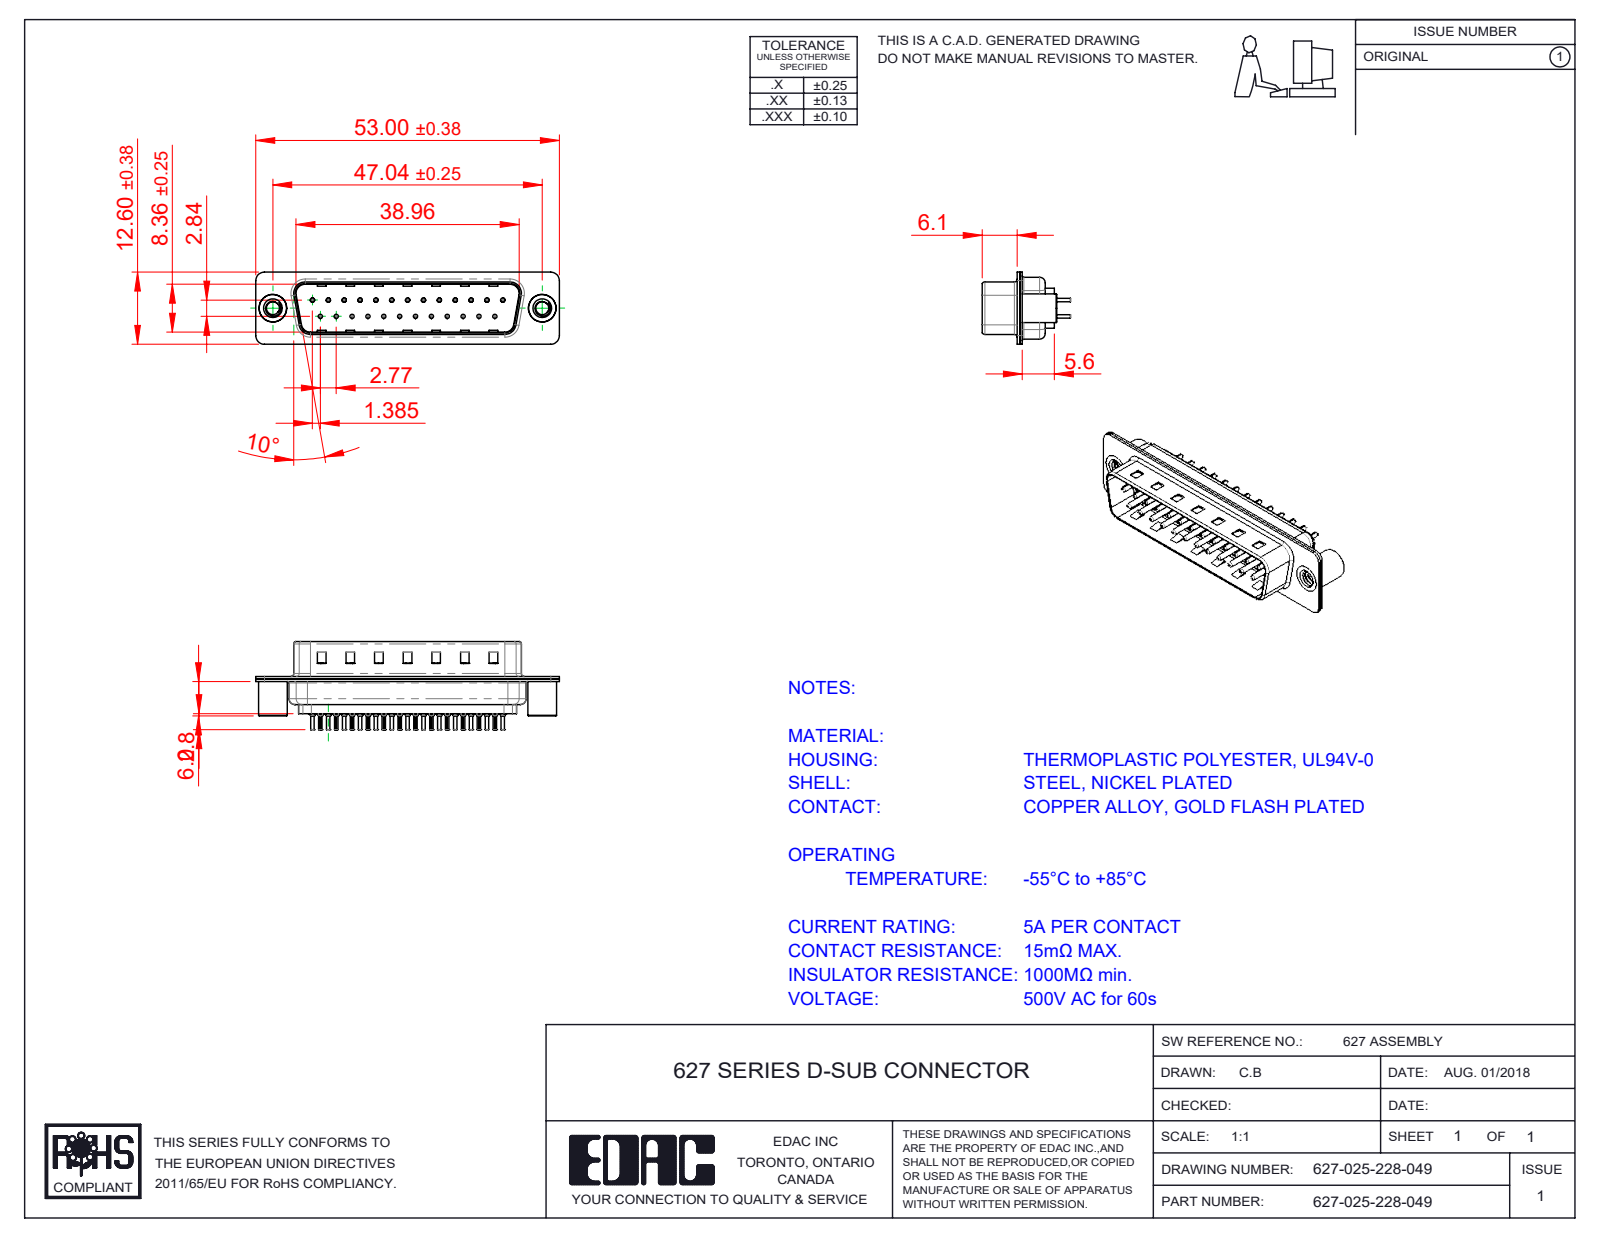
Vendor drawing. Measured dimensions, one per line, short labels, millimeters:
name: 627 Shell Rear_25 Contacts; 627 4-40 Threaded Standoff BS; 627 Shell Front_25 Contacts; 627 Contact Row 2_28L (+3 more)
written by: SolidWorks 2020 (CONFIG_CONTROL_DESIGN)
unit: mm
bodies: 31 solids, 2909 faces (777 planar, 1137 cylindrical, 995 other)
size: 53 × 18.8 × 12.6
volume: 3 374 mm³; area: 9 115 mm²
holes: 25× ⌀0.2, 25× ⌀0.35, 25× ⌀1.1, 25× ⌀1.6, 2× ⌀2.26, 2× ⌀4, 2× ⌀4.8
bosses: 25× ⌀2, 25× ⌀1.5, 25× ⌀0.75, 25× ⌀0.6, 2× ⌀5, 2× ⌀4.9
rounds: 50× R0.1, 16× R1.5, 12× R2, 8× R0.5, 8× R1.6, 4× R0.25, 4× R0.6, 4× R0.65
face distances: 0.4, 0.45, 6.05, 0.82, 9.58, 8.4, 1.5, 0.68, 7.68, 0.9
hole spacings: 3.16, 2.77, 5.54, 8.31, 11.08, 13.85, 5.04, 7.49
